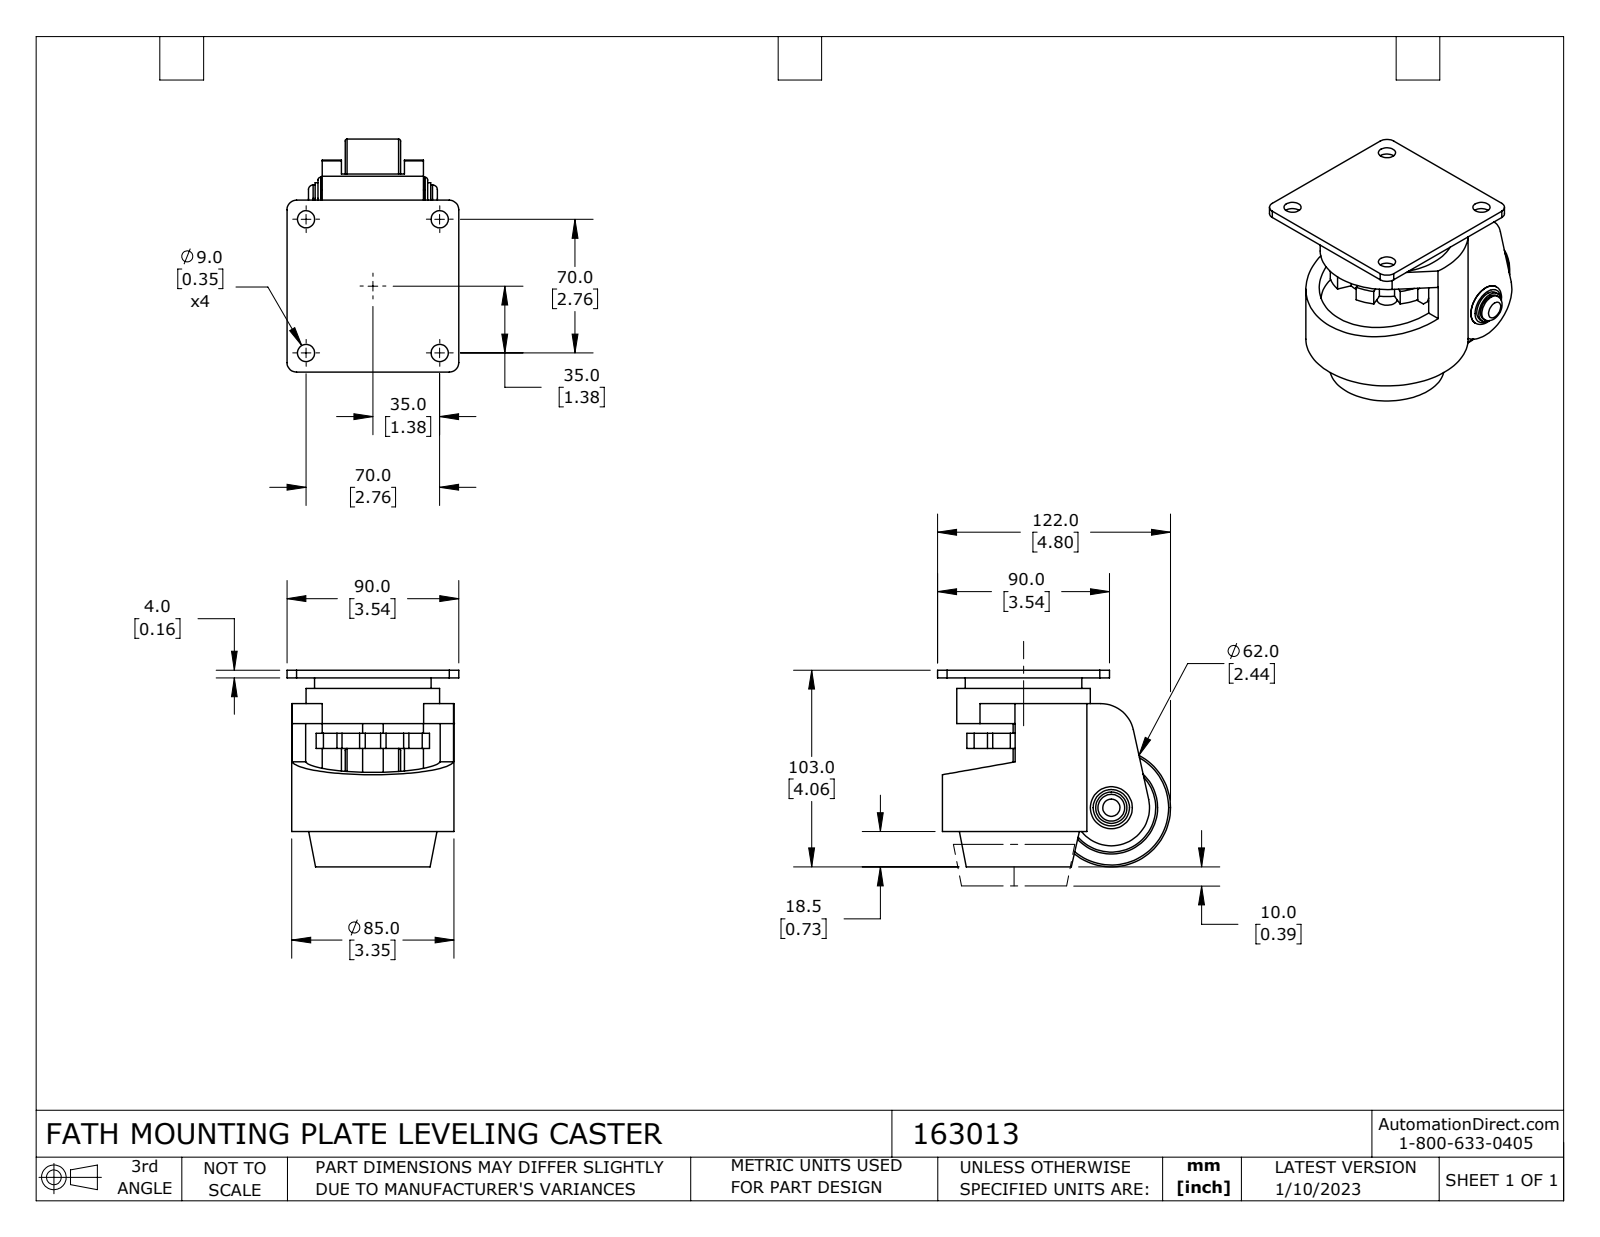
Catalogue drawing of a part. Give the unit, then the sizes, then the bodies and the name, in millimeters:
Units: millimetres
Overall size (bounding box): 122 × 103 × 90
Round holes (diameter × count): ⌀9 ×4, ⌀8.5 ×1, ⌀10 ×1, ⌀46.5 ×1
Round bosses / shafts (diameter × count): ⌀70 ×1, ⌀62 ×1, ⌀61.1 ×1, ⌀24 ×1, ⌀22 ×1, ⌀16.4 ×1, ⌀14 ×1, ⌀10.8 ×1
Partial cylindrical surfaces — rounded edges, fillets, slot ends (radius × count): R5 ×4, R17.4 ×1, R20 ×1, R23 ×1, R30.5 ×1, R34.5 ×1, R35.5 ×1, R42.5 ×1
Main face-to-face distances: 33, 10, 8, 4, 31, 41, 43, 13, 24, 28
Hole centre spacings: 49.5, 70, 99
Volume: 453 600 mm³ · Surface area: 98 260 mm²
Bodies: 1 solid, 167 faces (63 planar, 85 cylindrical, 19 other)
Part name (STEP PRODUCT): 163013
STEP written by: SolidWorks 2021 (CONFIG_CONTROL_DESIGN)
